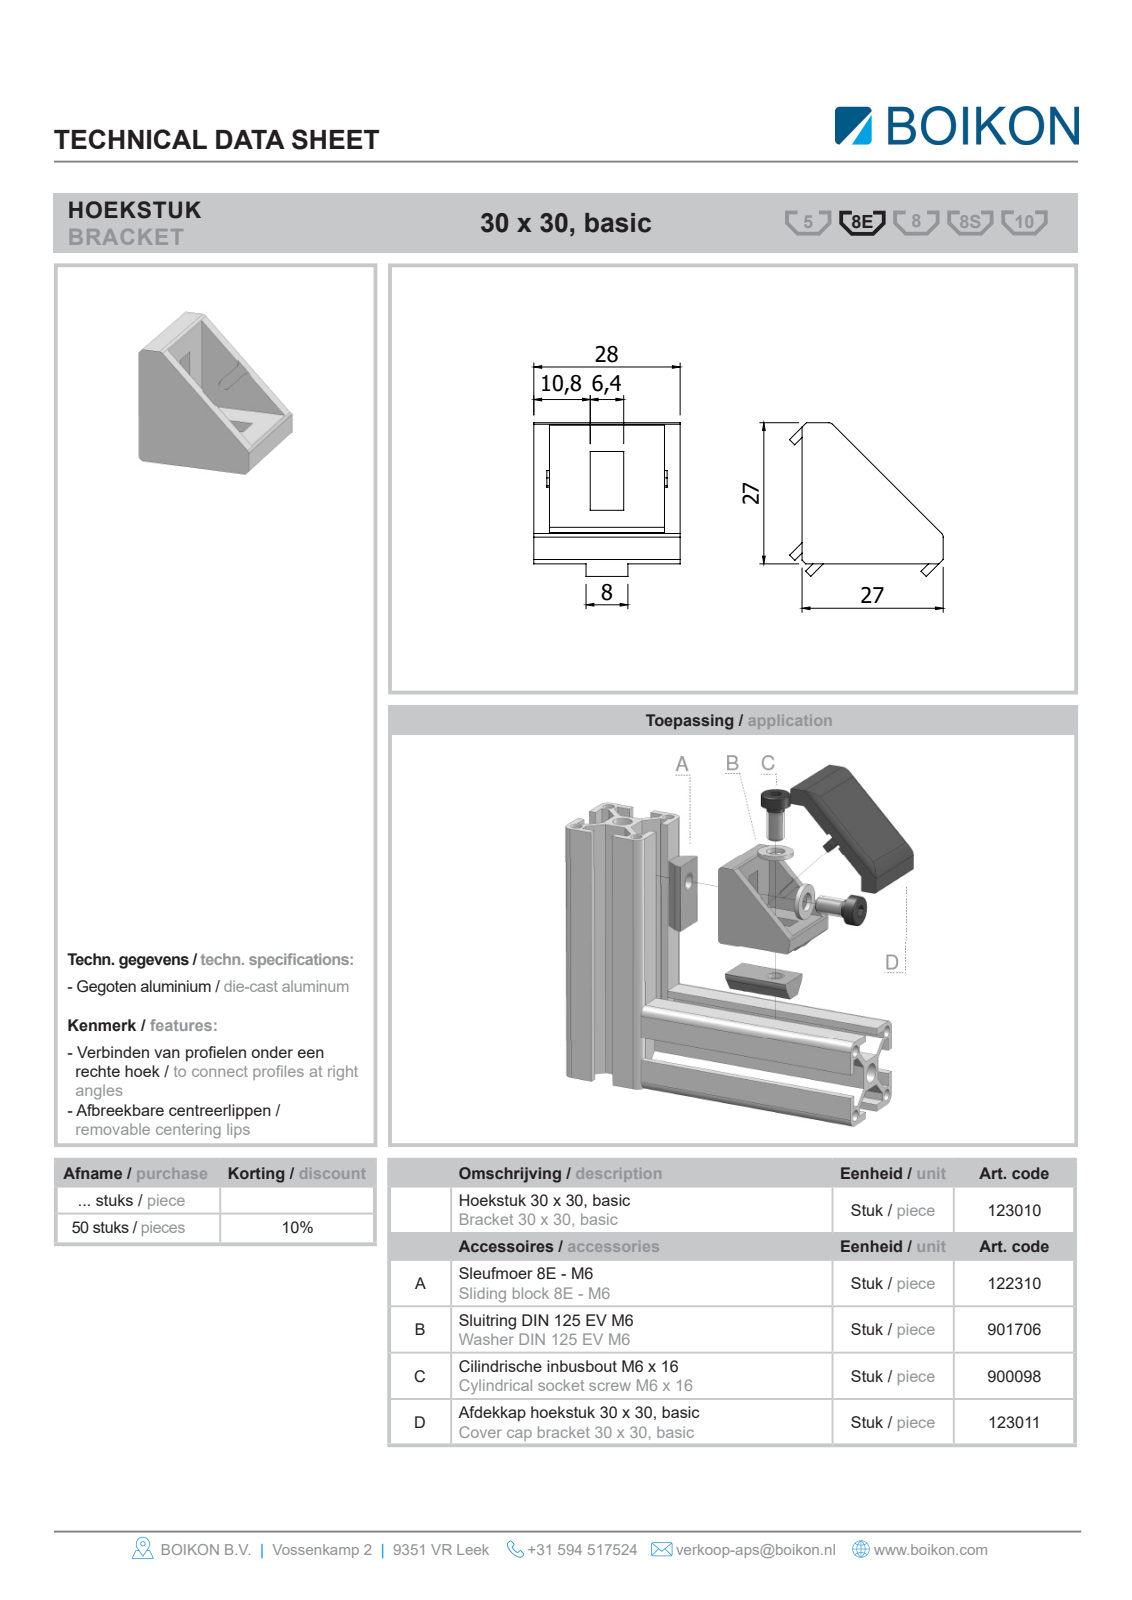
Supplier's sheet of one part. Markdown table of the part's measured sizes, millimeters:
| quantity | value |
| --- | --- |
| part name | Root; 123010HOEKSTUK 30X30 BASICBOIKON; 123011AFDEKKAP HOEKSTUK 30X30BOIKON; 902200Vlakke schroef M6x12BOIKON (+1 more) |
| STEP written by | HiCAD 2013 1802.4 Build 509 (AUTOMOTIVE_DESIGN) |
| units | millimeters |
| bodies | 6 solids, 195 faces (166 planar, 25 cylindrical, 4 other) |
| overall size | 42.02 × 42.02 × 28 |
| volume | 15 879 mm³ |
| surface area | 11 977 mm² |
| round holes (diameter × count) | 6 × 2 |
| round bosses / shafts (diameter × count) | 15 × 2, 4.77 × 2 |
| partial cylindrical surfaces (radius × count) | 4 × 6, 1 × 5, 2 × 2, 7 × 2, 1.25 × 1 |
| main face-to-face distances | 3, 6, 2.4, 8.4, 24.8, 10.8, 25, 2.8, 17, 28 |
